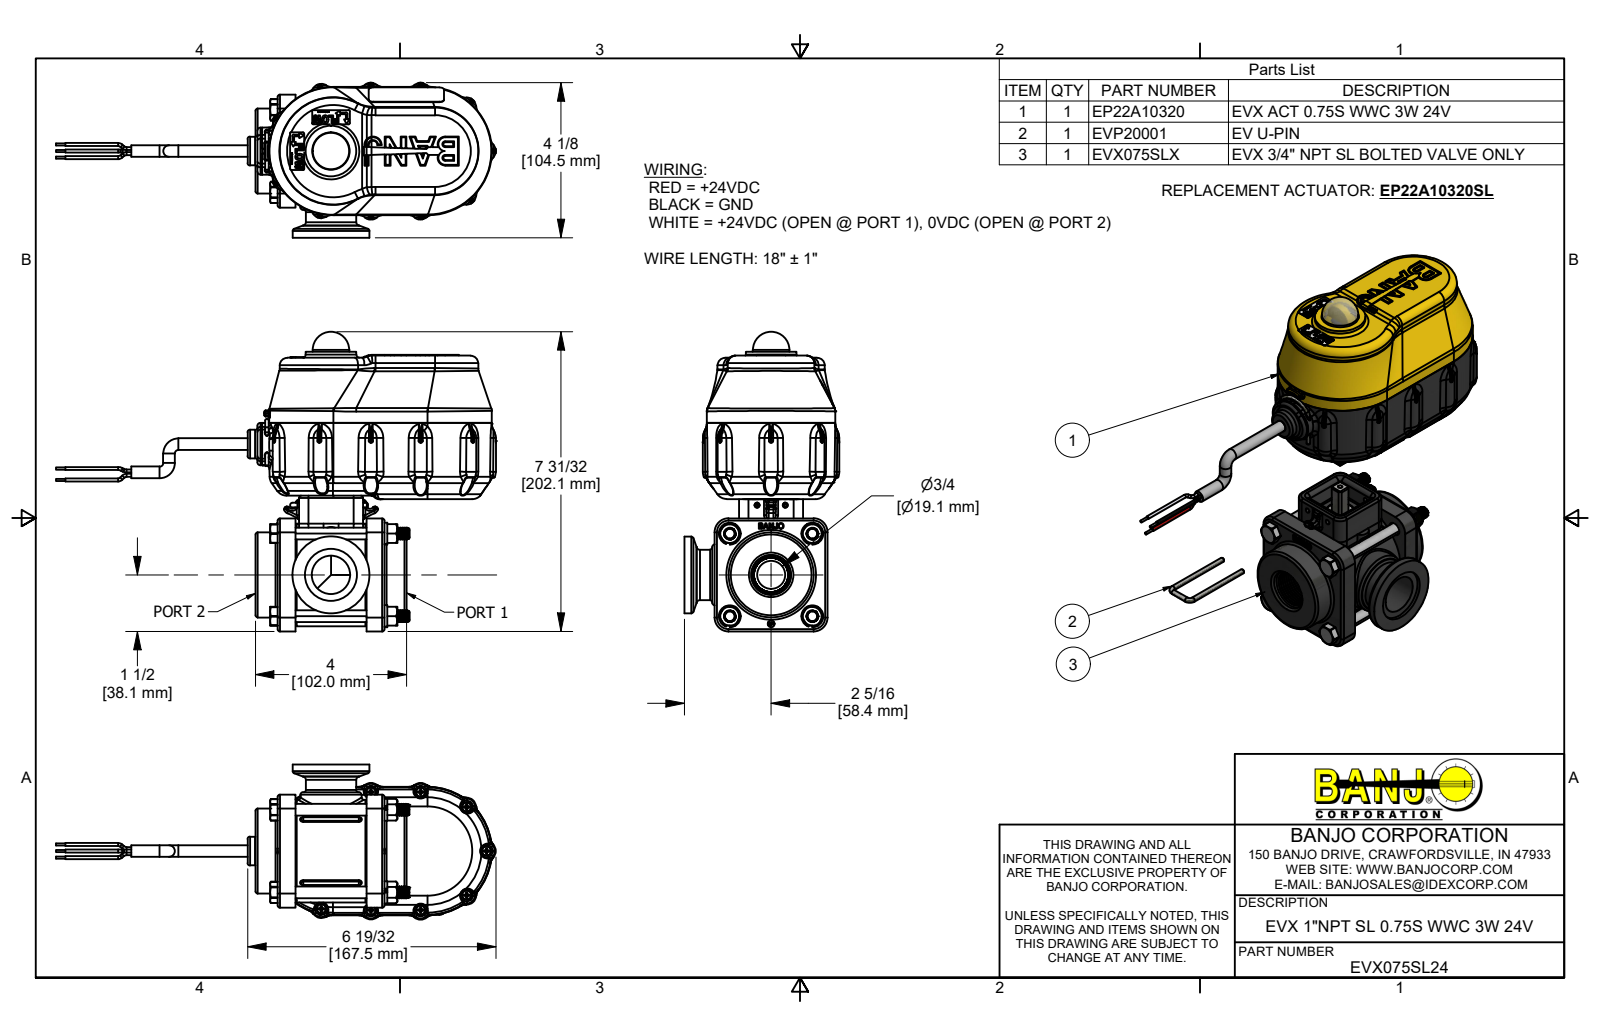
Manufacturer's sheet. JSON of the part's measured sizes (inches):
{"part_name": "EVX075SL24; EP22A10320; B61905PPHS; B632038PM (+8 more)", "step_written_by": "Autodesk Inventor 2021 (AUTOMOTIVE_DESIGN)", "units": "inches", "bodies": {"solids": 98, "faces": 12132, "planar": 3301, "cylindrical": 3481, "other": 5350}, "overall_size": [11.685, 7.957, 4.115], "volume_in3": 53.93, "surface_area_in2": 593.2, "round_holes": [[0.095, 11], [0.15, 11], [0.08, 7], [0.107, 4], [0.126, 4], [0.136, 4], [0.148, 4], [0.15, 4], [0.17, 4], [0.252, 4], [0.322, 4], [0.365, 4]], "round_bosses_or_shafts": [[0.268, 60], [0.25, 17], [0.08, 15], [0.14, 11], [0.108, 11], [0.085, 11], [0.058, 6], [0.313, 5]], "partial_cylinders_radius": [[0.013, 180], [0.04, 145], [0.01, 84], [0.02, 72], [0.06, 58], [0.005, 53], [0.03, 38], [0.08, 28]], "face_to_face_distances": [0.1, 2.565, 0.055, 0.211, 0.06, 0.151, 2.36, 0.475, 2.95, 0.125], "hole_center_spacings": [1.55, 2.192, 2.656, 1.046, 1.513, 1.662, 1.891, 2.69]}
